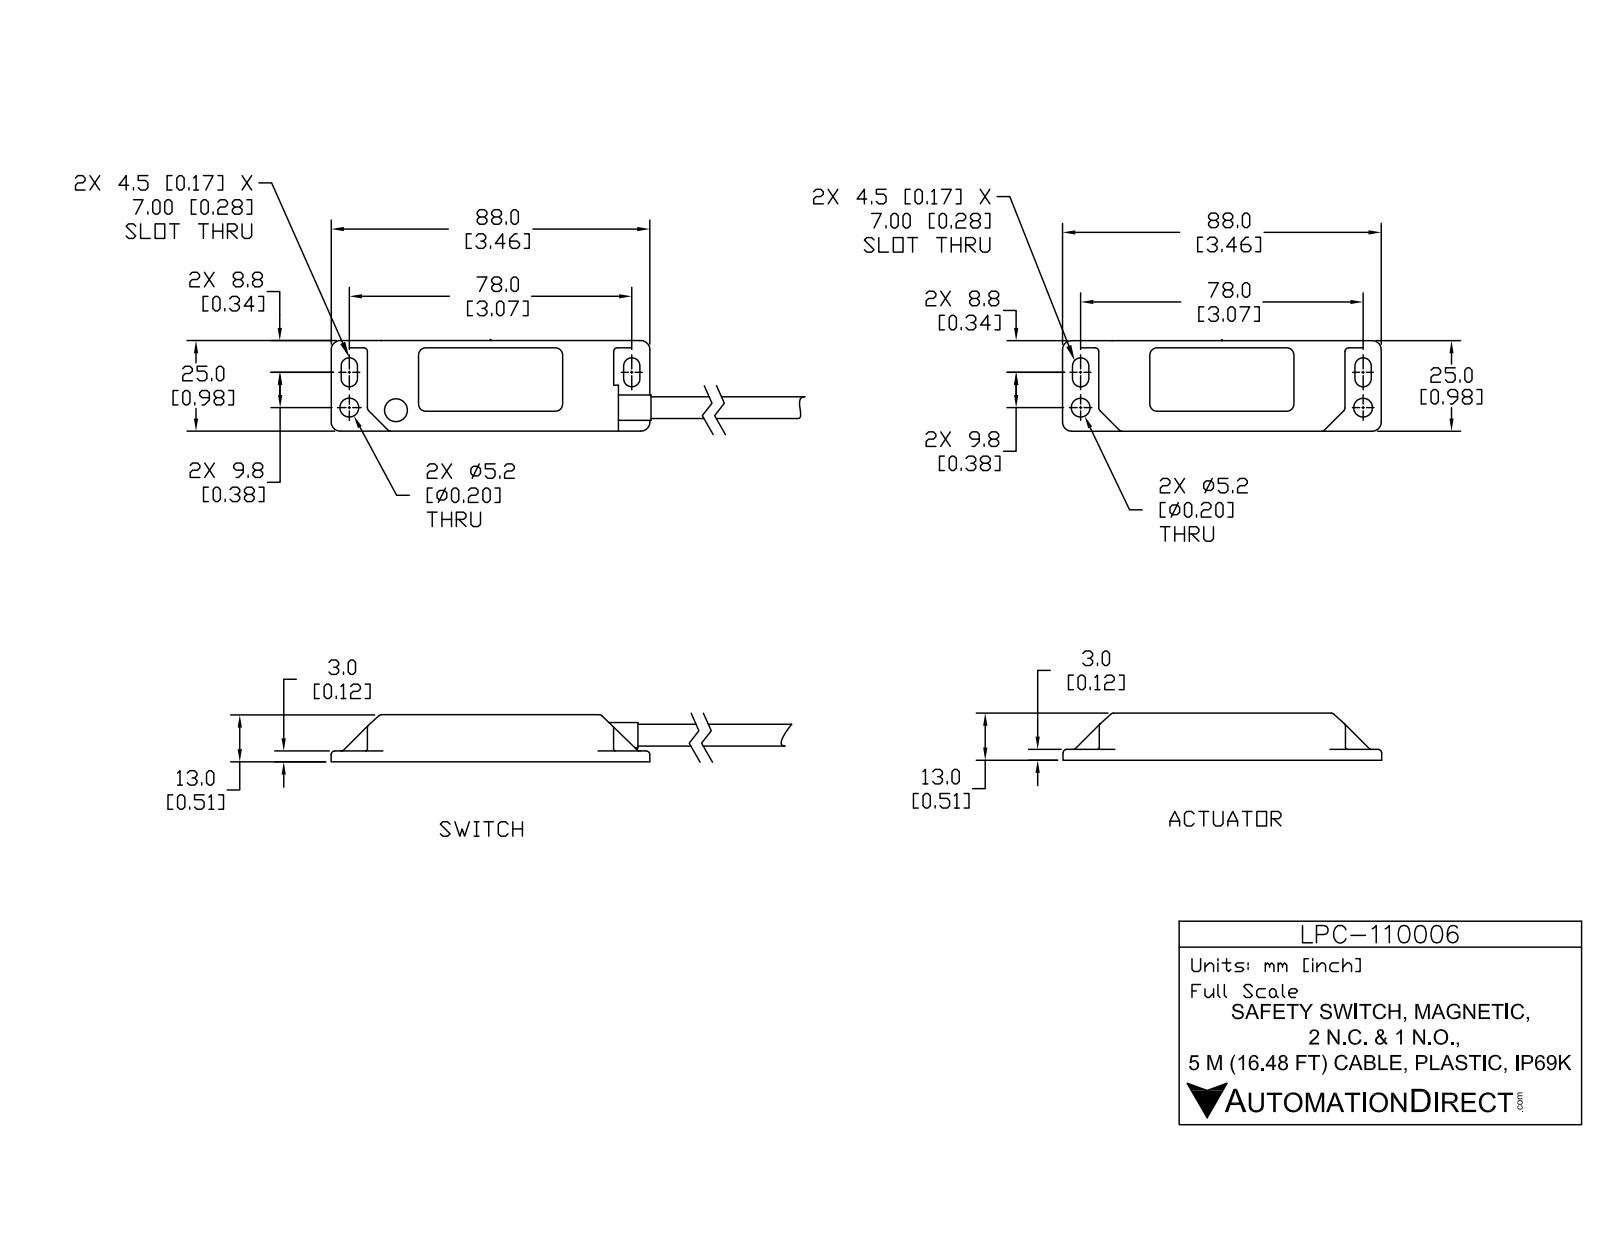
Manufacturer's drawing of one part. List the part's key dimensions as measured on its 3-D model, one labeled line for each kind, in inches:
Part name (STEP PRODUCT): LPC-110006; LPC-110006_2; LPC-110006_1
STEP written by: SolidWorks 2017 (AUTOMOTIVE_DESIGN)
Units: inches
Bodies: 11 solids, 1058 faces (401 planar, 303 cylindrical, 354 other)
Overall size (bounding box): 10.221 × 1.992 × 0.543
Volume: 1.698 in³ · Surface area: 47.9 in²
Round holes (diameter × count): ⌀0.197 ×4, ⌀0.205 ×4, ⌀0.119 ×1, ⌀0.173 ×1, ⌀0.213 ×1, ⌀0.232 ×1, ⌀0.276 ×1
Round bosses / shafts (diameter × count): ⌀0.079 ×4, ⌀0.193 ×2, ⌀0.091 ×2, ⌀0.339 ×1, ⌀0.299 ×1, ⌀0.28 ×1, ⌀0.236 ×1, ⌀0.209 ×1
Partial cylindrical surfaces — rounded edges, fillets, slot ends (radius × count): R0.02 ×116, R0.039 ×49, R0.079 ×10, R0.089 ×8, R0.098 ×8, R0.012 ×6, R0.189 ×1
Main face-to-face distances: 0.067, 0.441, 0.079, 0.374, 0.059, 0.071, 0.508, 0.445, 0.512, 0.988
Hole centre spacings: 0.748, 1.097, 1.19, 1.275, 1.48, 1.571, 1.784, 1.895
